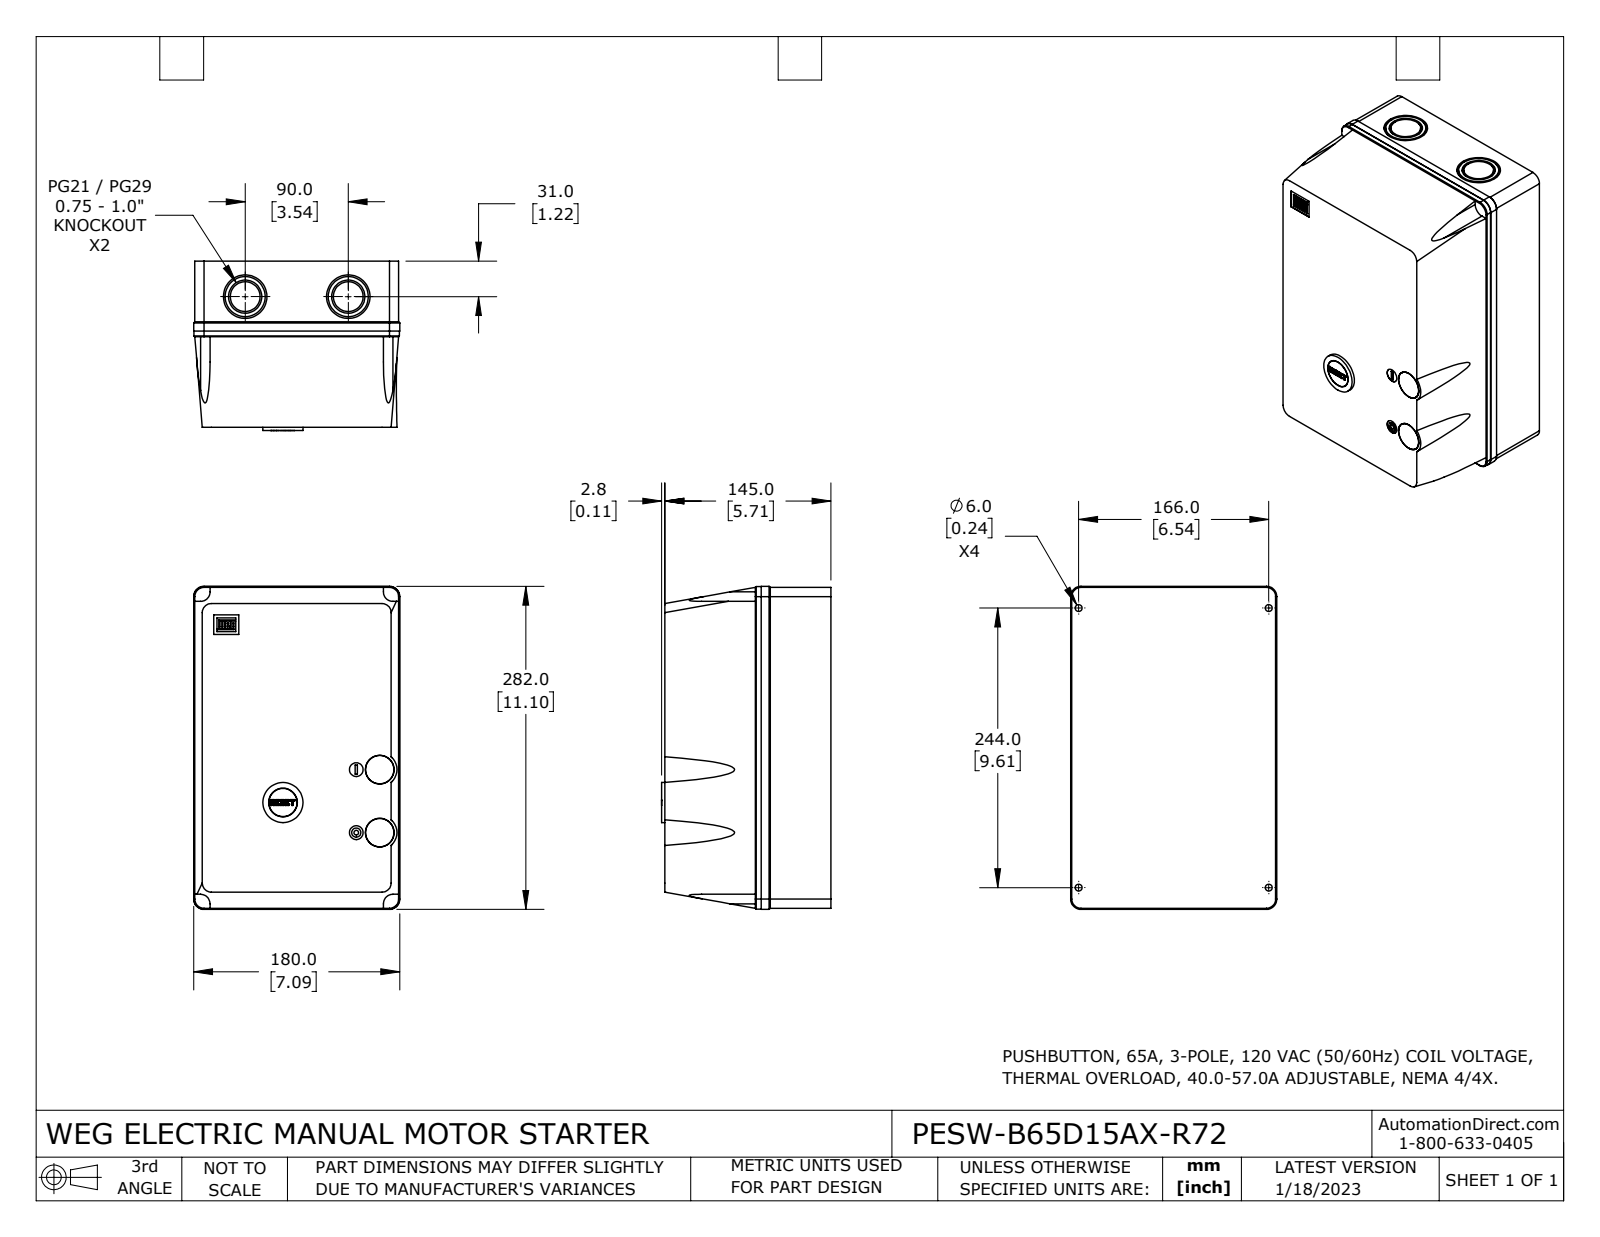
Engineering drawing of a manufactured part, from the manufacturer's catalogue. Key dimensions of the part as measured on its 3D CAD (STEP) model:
Part name (STEP PRODUCT): PESW-B65D15AX-R72
STEP written by: SolidWorks 2021 (CONFIG_CONTROL_DESIGN)
Units: millimetres
Bodies: 3 solids, 286 faces (130 planar, 144 cylindrical, 12 other)
Overall size (bounding box): 282 × 180 × 147.9
Volume: 7 014 000 mm³ · Surface area: 232 257 mm²
Round holes (diameter × count): ⌀6 ×4, ⌀25 ×3, ⌀12 ×2, ⌀29 ×2, ⌀38 ×2, ⌀4 ×1, ⌀30.5 ×1
Round bosses / shafts (diameter × count): ⌀35 ×3, ⌀26 ×2, ⌀24.8 ×2, ⌀30.3 ×1, ⌀24.6 ×1, ⌀14 ×1, ⌀8 ×1
Partial cylindrical surfaces — rounded edges, fillets, slot ends (radius × count): R0.1 ×34, R8 ×4, R8.3 ×4, R8.7 ×4, R9 ×4, R1.6 ×1
Main face-to-face distances: 145, 178, 280, 1, 0.7, 179, 179.7, 178.7, 281, 180
Hole centre spacings: 20.5, 55, 58.7, 166, 244, 295.11, 49.14, 57.14
